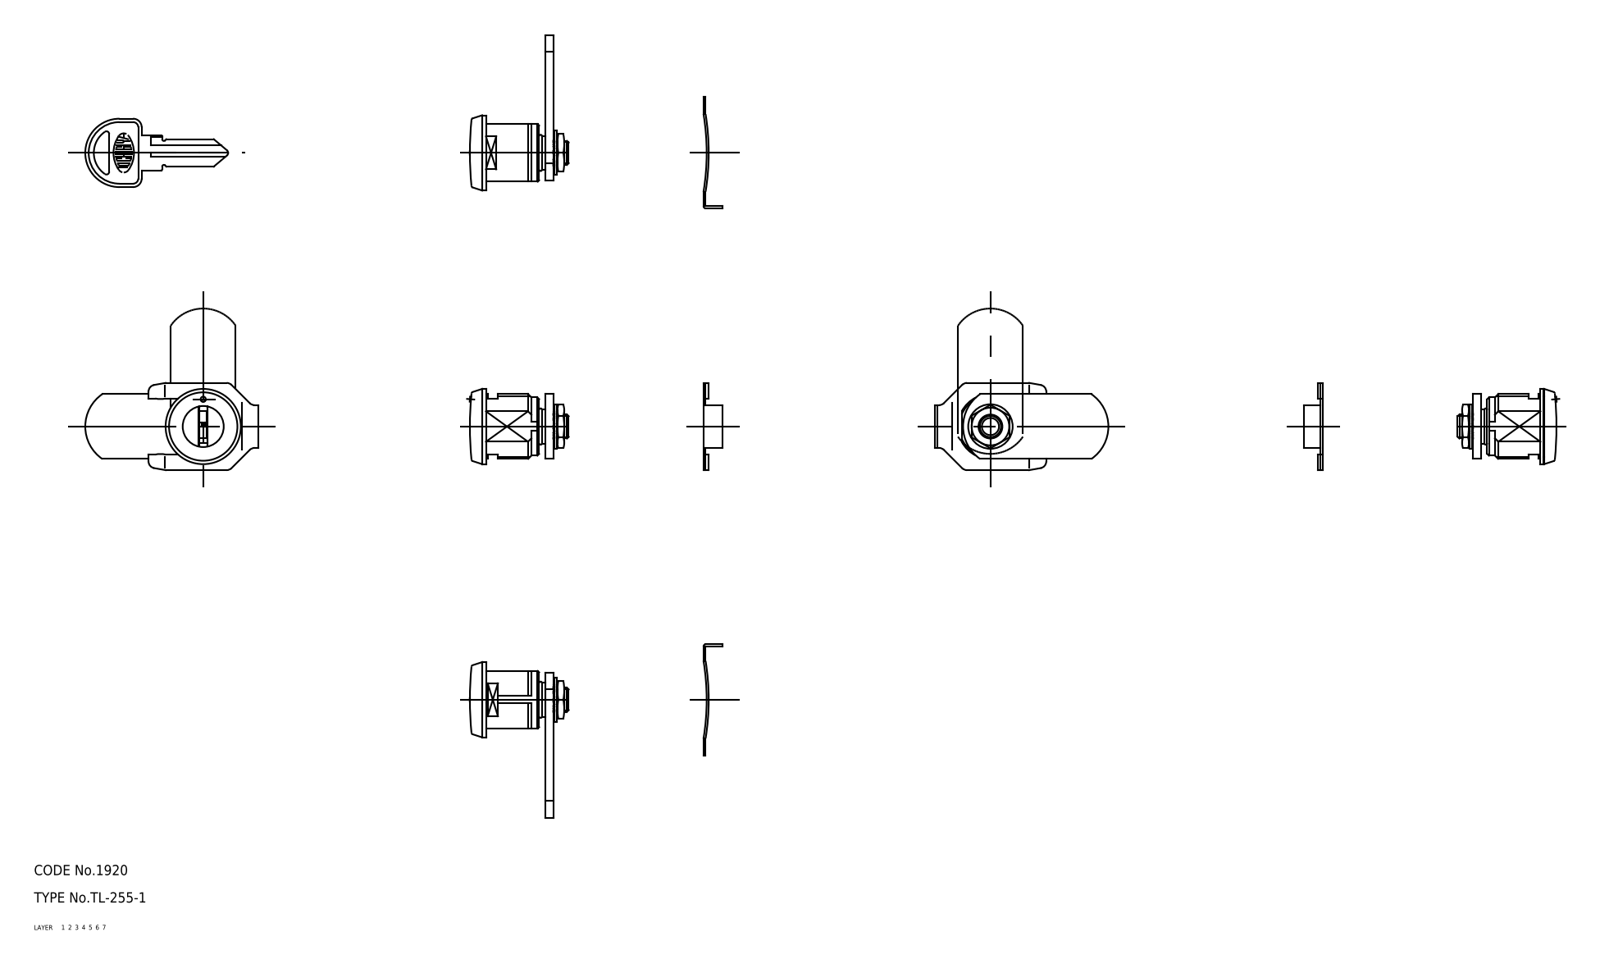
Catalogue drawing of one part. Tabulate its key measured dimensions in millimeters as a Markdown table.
| quantity | value |
| --- | --- |
| part name | retainer; washer; nut_B; lock (+4 more) |
| STEP written by | CADfix (AUTOMOTIVE_DESIGN) |
| units | millimeters |
| bodies | 7 solids, 181 faces (0 planar, 0 cylindrical, 181 other) |
| overall size | 110.4 × 50.7 × 25.5 |
| volume | 8 603 mm³ |
| surface area | 7 448 mm² |
